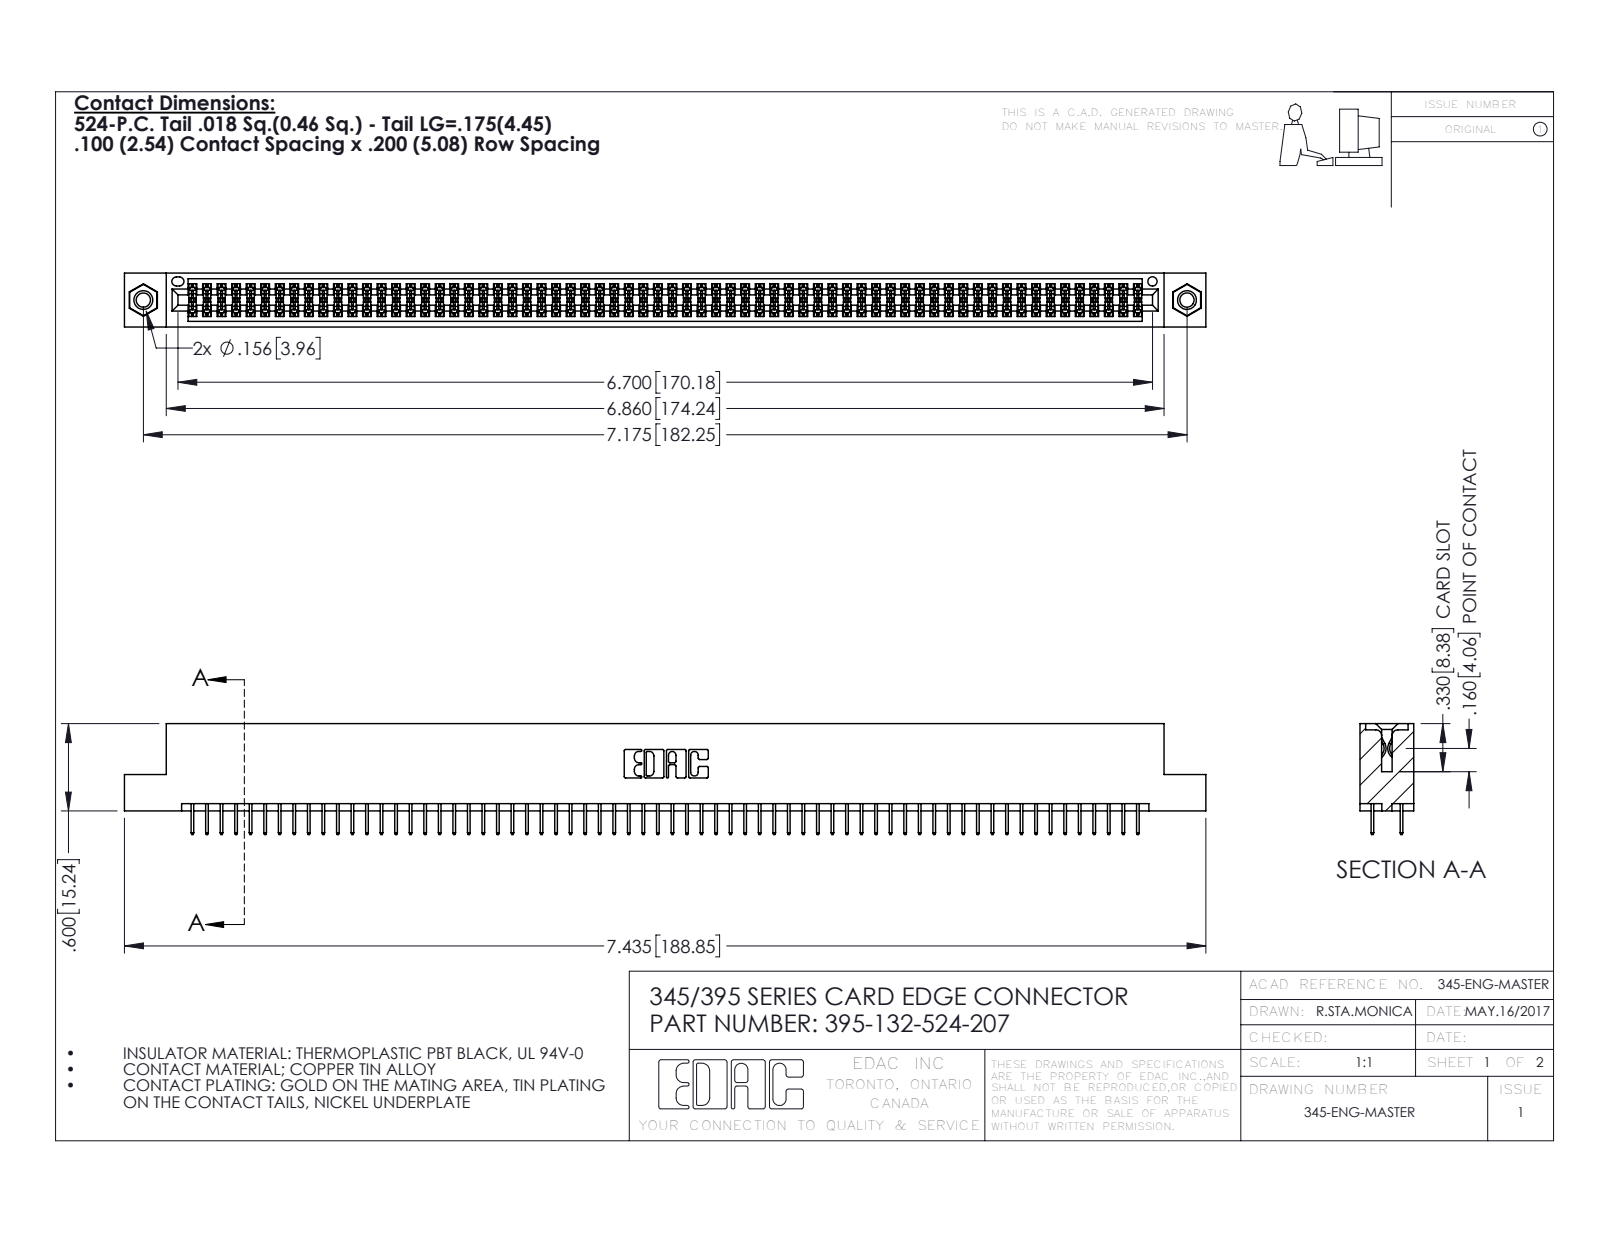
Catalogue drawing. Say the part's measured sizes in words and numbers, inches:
The part is named "345 Part_Flush Mounting Lugs - 0.156 Dia-TI; 395-132-524-207; 345-292-001_345-293-124; 345-250-001_345-250-005-103". Its 3-D file was written by "SolidWorks 2016 (CONFIG_CONTROL_DESIGN)". It is 135 solids with 7314 faces: 5260 planar, 2038 cylindrical and 16 other. Overall it measures 7.435 by 0.762 by 0.37 inches. Its volume is 1.12 cubic inches and its surface area 42 square inches. Round holes: 2 of diameter 0.098, 2 of diameter 0.125, 2 of diameter 0.156, 1 of diameter 0.064. Round bosses or shafts: 2 of diameter 0.155. Partial cylindrical surfaces (rounded edges, fillets, slot ends): 198 of radius 0.006, 22 of radius 0.01, 6 of radius 0.007, 6 of radius 0.031, 3 of radius 0.026, 2 of radius 0.014, 2 of radius 0.019, 2 of radius 0.022. The main face-to-face distances are 0.072, 0.298, 0.2, 0.37, 0.098, 0.272, 0.025, 0.225, 0.072, 0.175. The hole center spacings are 0.27, 6.939, 7.175.
